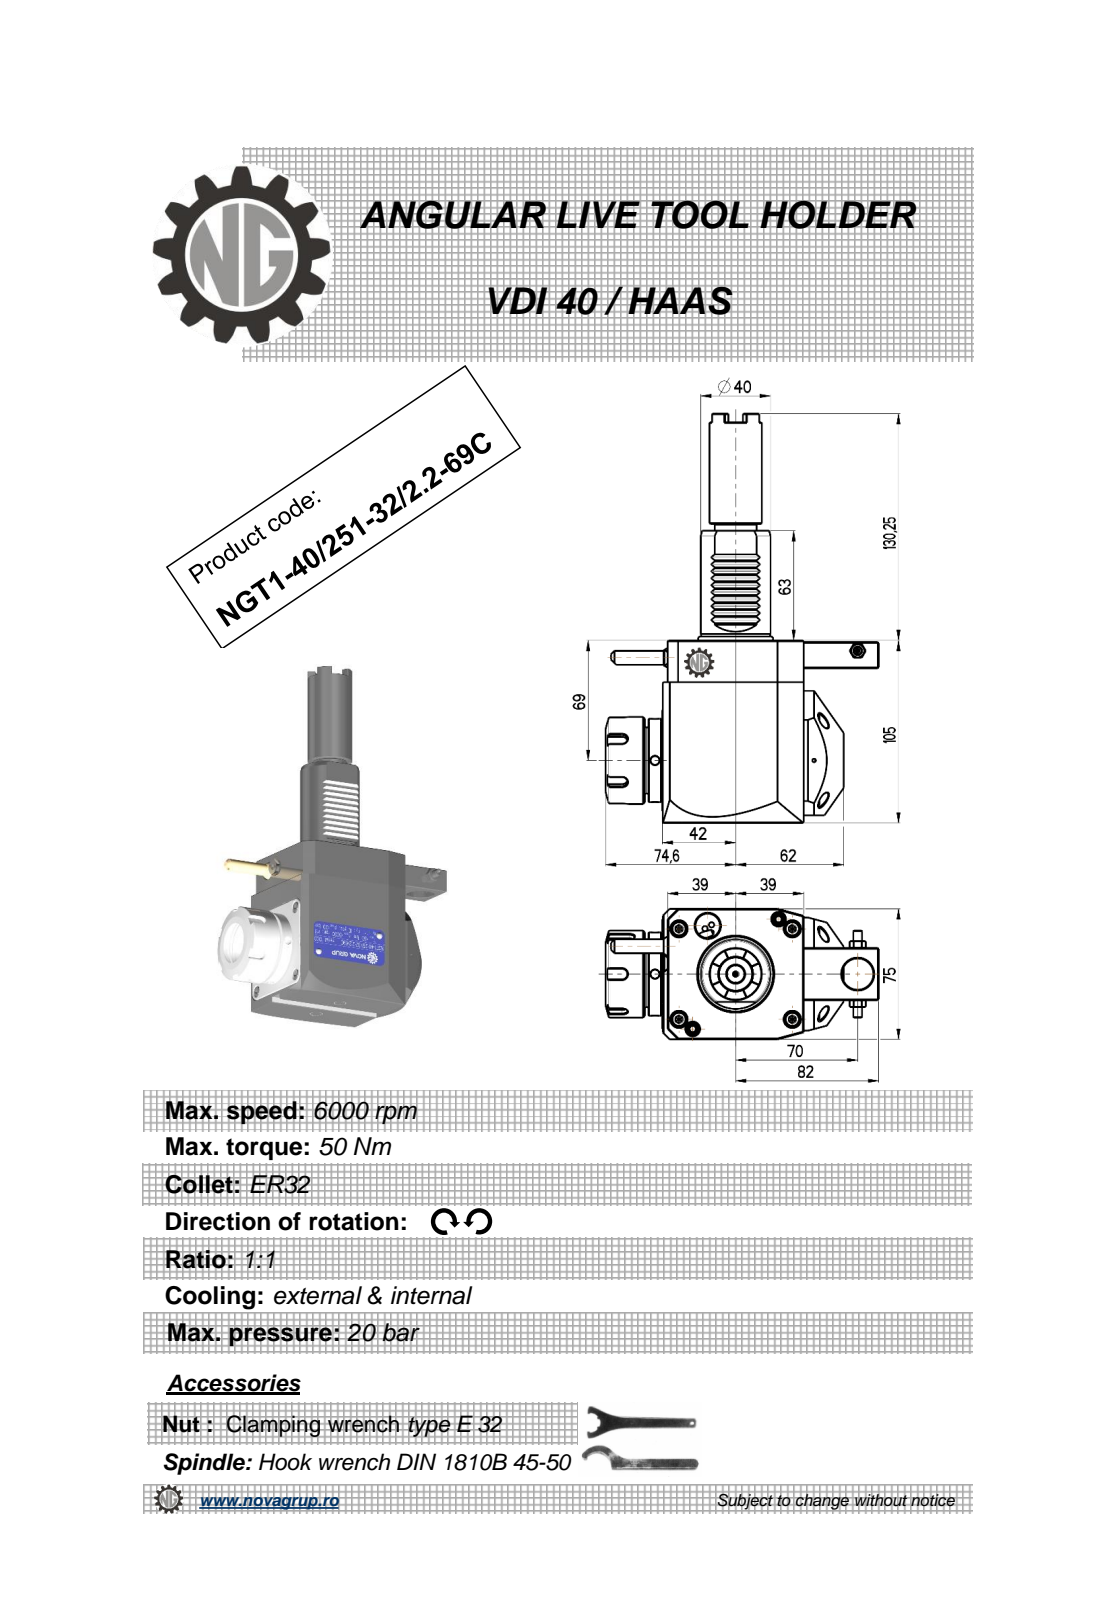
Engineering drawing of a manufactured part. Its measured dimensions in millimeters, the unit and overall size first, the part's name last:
Units: millimetres
Overall size (bounding box): 235.25 × 156.6 × 76.6
Round holes (diameter × count): ⌀5 ×3, ⌀3 ×1, ⌀4.2 ×1, ⌀9.5 ×1, ⌀18 ×1, ⌀19.5 ×1, ⌀27 ×1
Round bosses / shafts (diameter × count): ⌀50 ×1, ⌀48 ×1, ⌀41 ×1, ⌀40 ×1, ⌀30 ×1, ⌀24 ×1, ⌀10 ×1, ⌀8.96 ×1
Partial cylindrical surfaces — rounded edges, fillets, slot ends (radius × count): R0.26 ×12, R0.3 ×10, R0.2 ×6, R3 ×5, R0.5 ×1, R40 ×1
Main face-to-face distances: 75, 105, 81, 104, 80.8, 1, 101, 22.5, 3, 89
Hole centre spacings: 16.19, 46.25, 61.13, 61.5, 70, 116.25, 132.22
Volume: 873 052 mm³ · Surface area: 76 351 mm²
Bodies: 1 solid, 459 faces (226 planar, 92 cylindrical, 141 other)
Part name (STEP PRODUCT): NGT1_40_251_32_2_2_69C
STEP written by: PRO/ENGINEER BY PARAMETRIC TECHNOLOGY CORPORATION, 2010280 (CONFIG_CONTROL_DESIGN)
